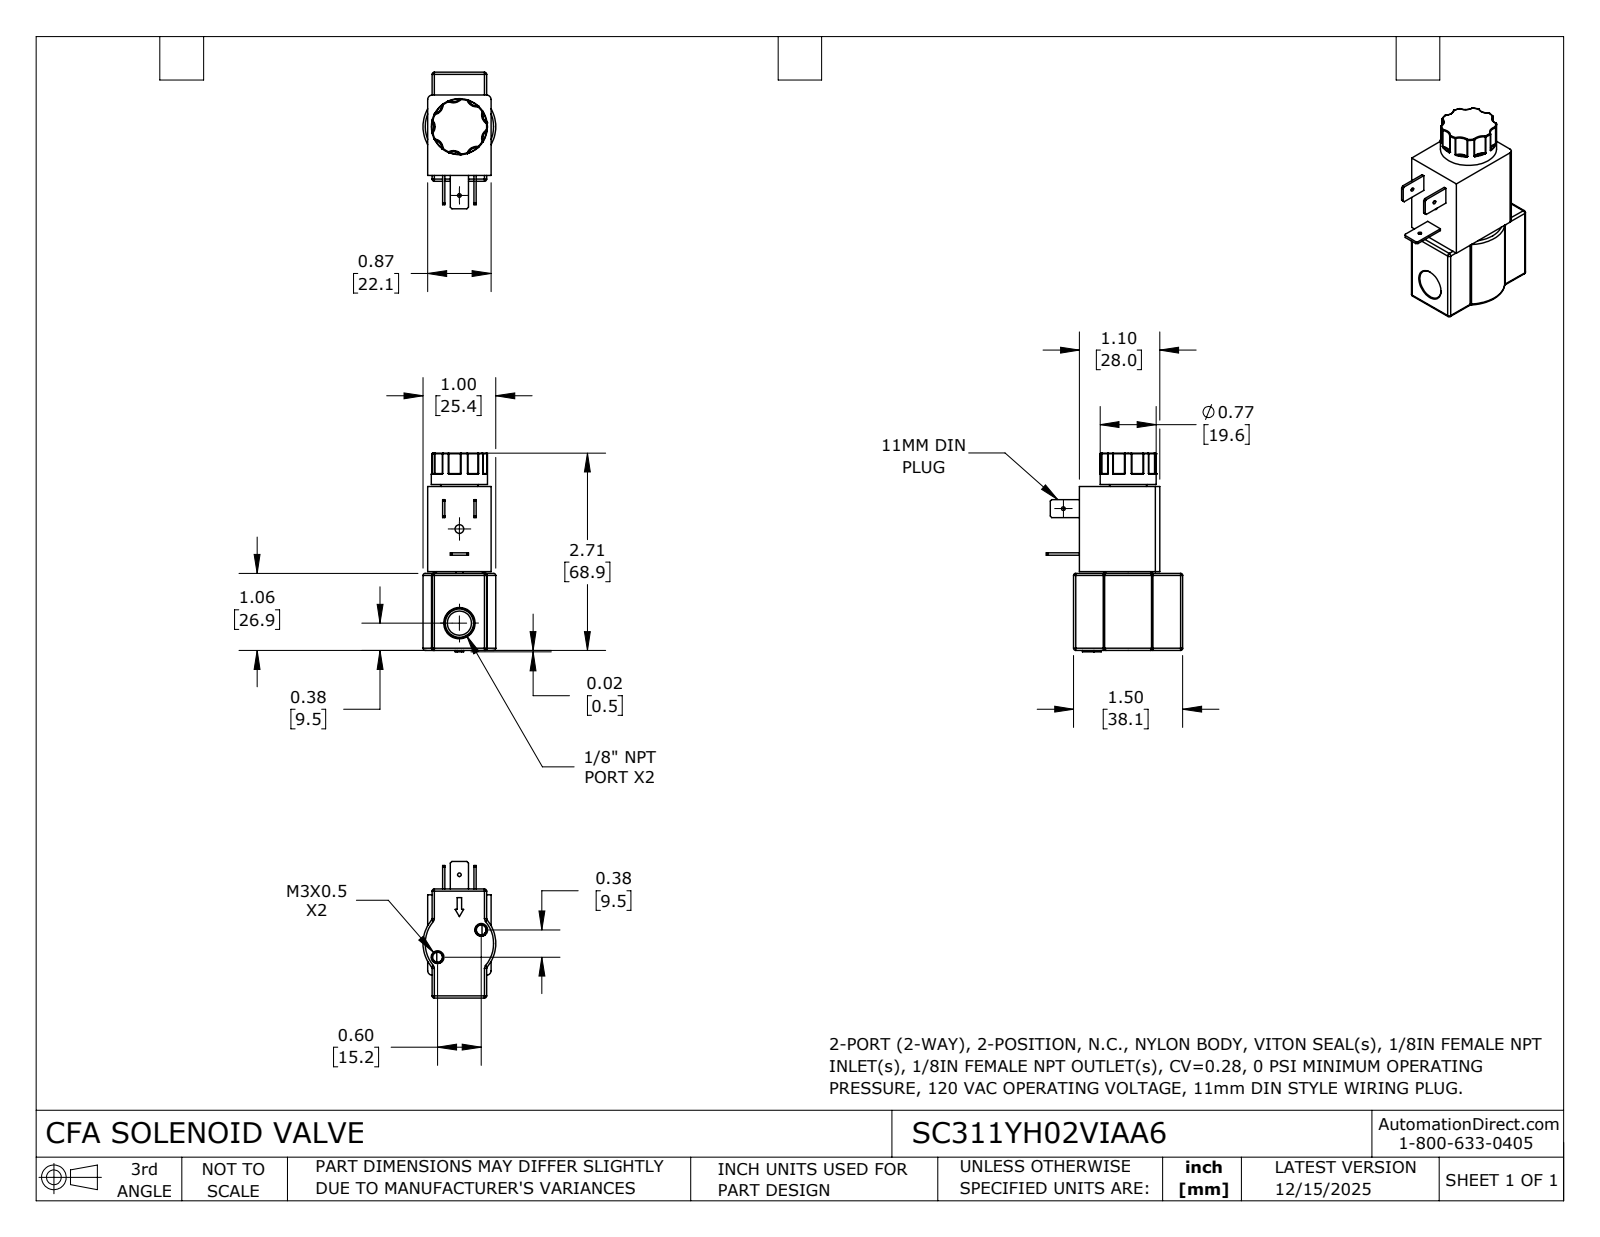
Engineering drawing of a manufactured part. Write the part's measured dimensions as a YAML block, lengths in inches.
part_name: "SC311YH02VIAA6"
step_written_by: "SolidWorks 2024 (CONFIG_CONTROL_DESIGN)"
units: inches
bodies: {solids: 1, faces: 383, planar: 62, cylindrical: 117, other: 204}
overall_size: [2.732, 1.877, 1]
volume: 2.516
surface_area: 17.12
round_holes:
  - {diameter: 0.05, count: 2}
  - {diameter: 0.136, count: 2}
  - {diameter: 0.12, count: 1}
  - {diameter: 0.332, count: 1}
round_bosses_or_shafts:
  - {diameter: 0.77, count: 1}
partial_cylinders:
  - {radius: 0.01, count: 18}
  - {radius: 0.03, count: 16}
  - {radius: 0.133, count: 7}
  - {radius: 0.06, count: 2}
  - {radius: 0.132, count: 2}
  - {radius: 0.295, count: 2}
  - {radius: 0.311, count: 1}
  - {radius: 0.5, count: 1}
face_to_face_distances: [0.06, 0.81, 0.87, 1.104, 2.252, 1.06, 1.192, 0.75, 1.085, 0.025]
hole_center_spacings: [0.707, 0.815, 1.172, 1.293]
